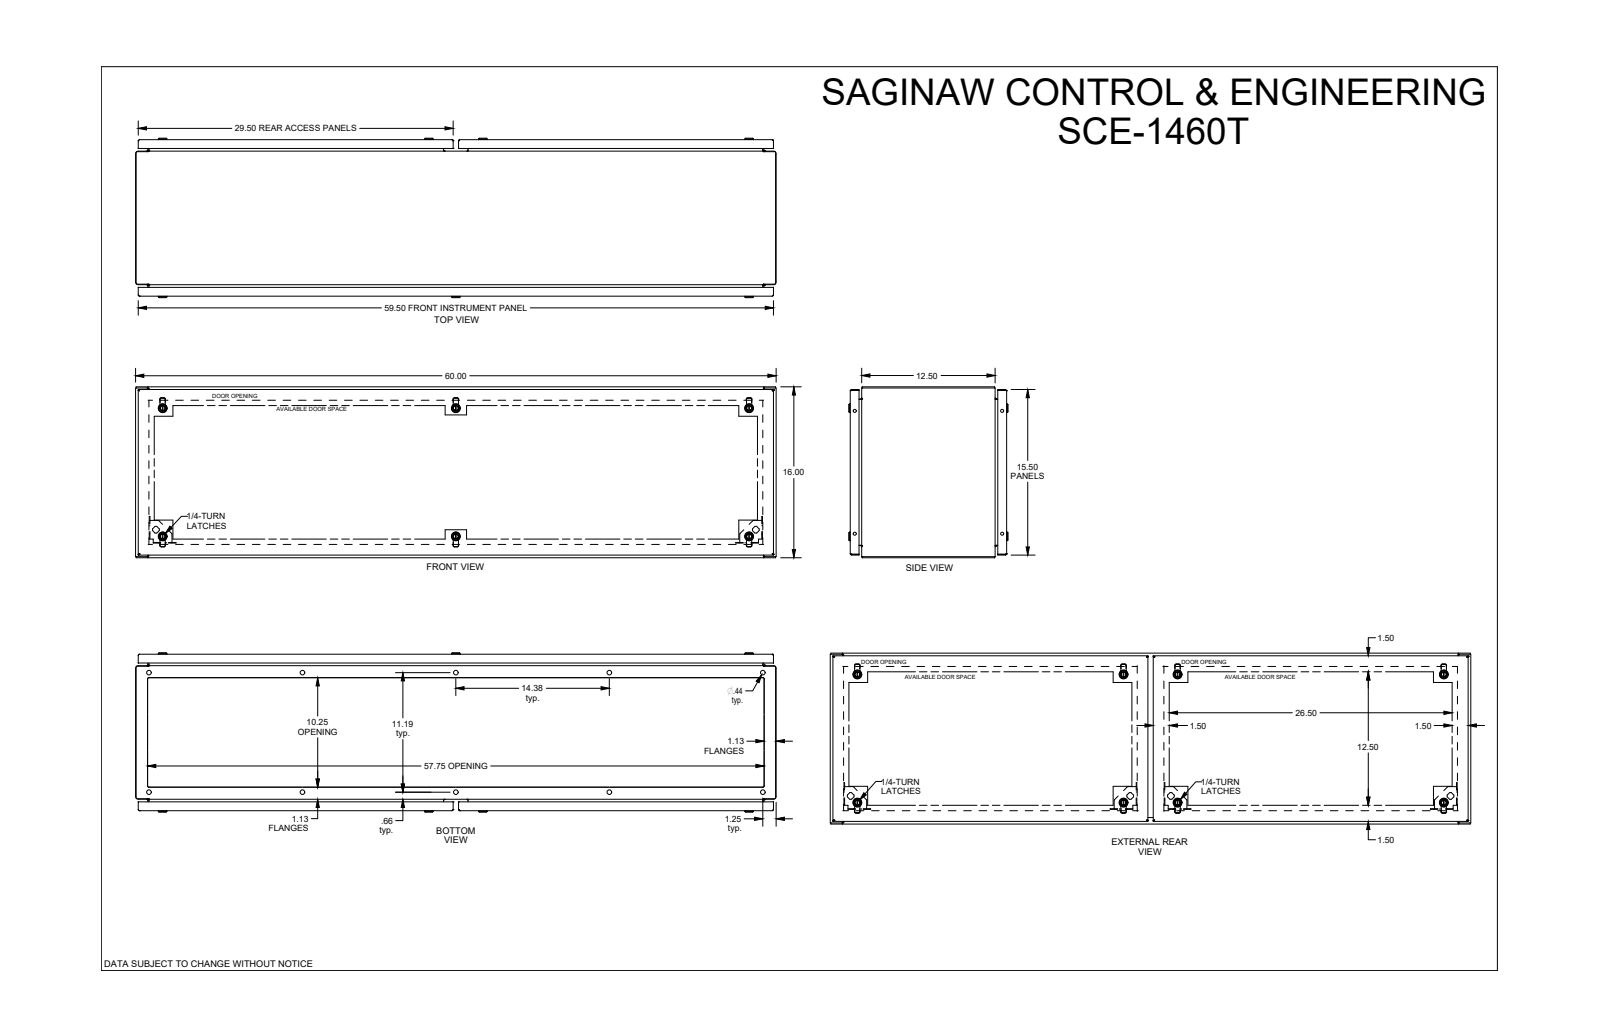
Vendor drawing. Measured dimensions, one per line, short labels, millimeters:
name: SCE-1460T
written by: SolidWorks 2019 (AUTOMOTIVE_DESIGN)
unit: mm
bodies: 87 solids, 5245 faces (2519 planar, 2100 cylindrical, 626 other)
size: 1524 × 406.4 × 379.1
volume: 5 908 000 mm³; area: 5 562 000 mm²
holes: 10× ⌀4.2, 10× ⌀6, 10× ⌀8.1, 10× ⌀11.1, 10× ⌀12, 10× ⌀16.1
bosses: 10× ⌀21, 10× ⌀20, 10× ⌀14, 10× ⌀11.8, 10× ⌀10.8, 10× ⌀9.2, 10× ⌀8, 10× ⌀4.8
rounds: 252× R0.3, 112× R0.5, 110× R0.5, 37× R3.2, 30× R0.4, 28× R2.6, 28× R3.4, 28× R5.9
face distances: 1.5, 370.5, 2.6, 372.1, 369, 1521.4, 29.1, 374.7, 403.8, 27.3
hole spacings: 462.7, 284.1, 304.8, 64.3, 311.5, 365.1, 365.1, 633.4
